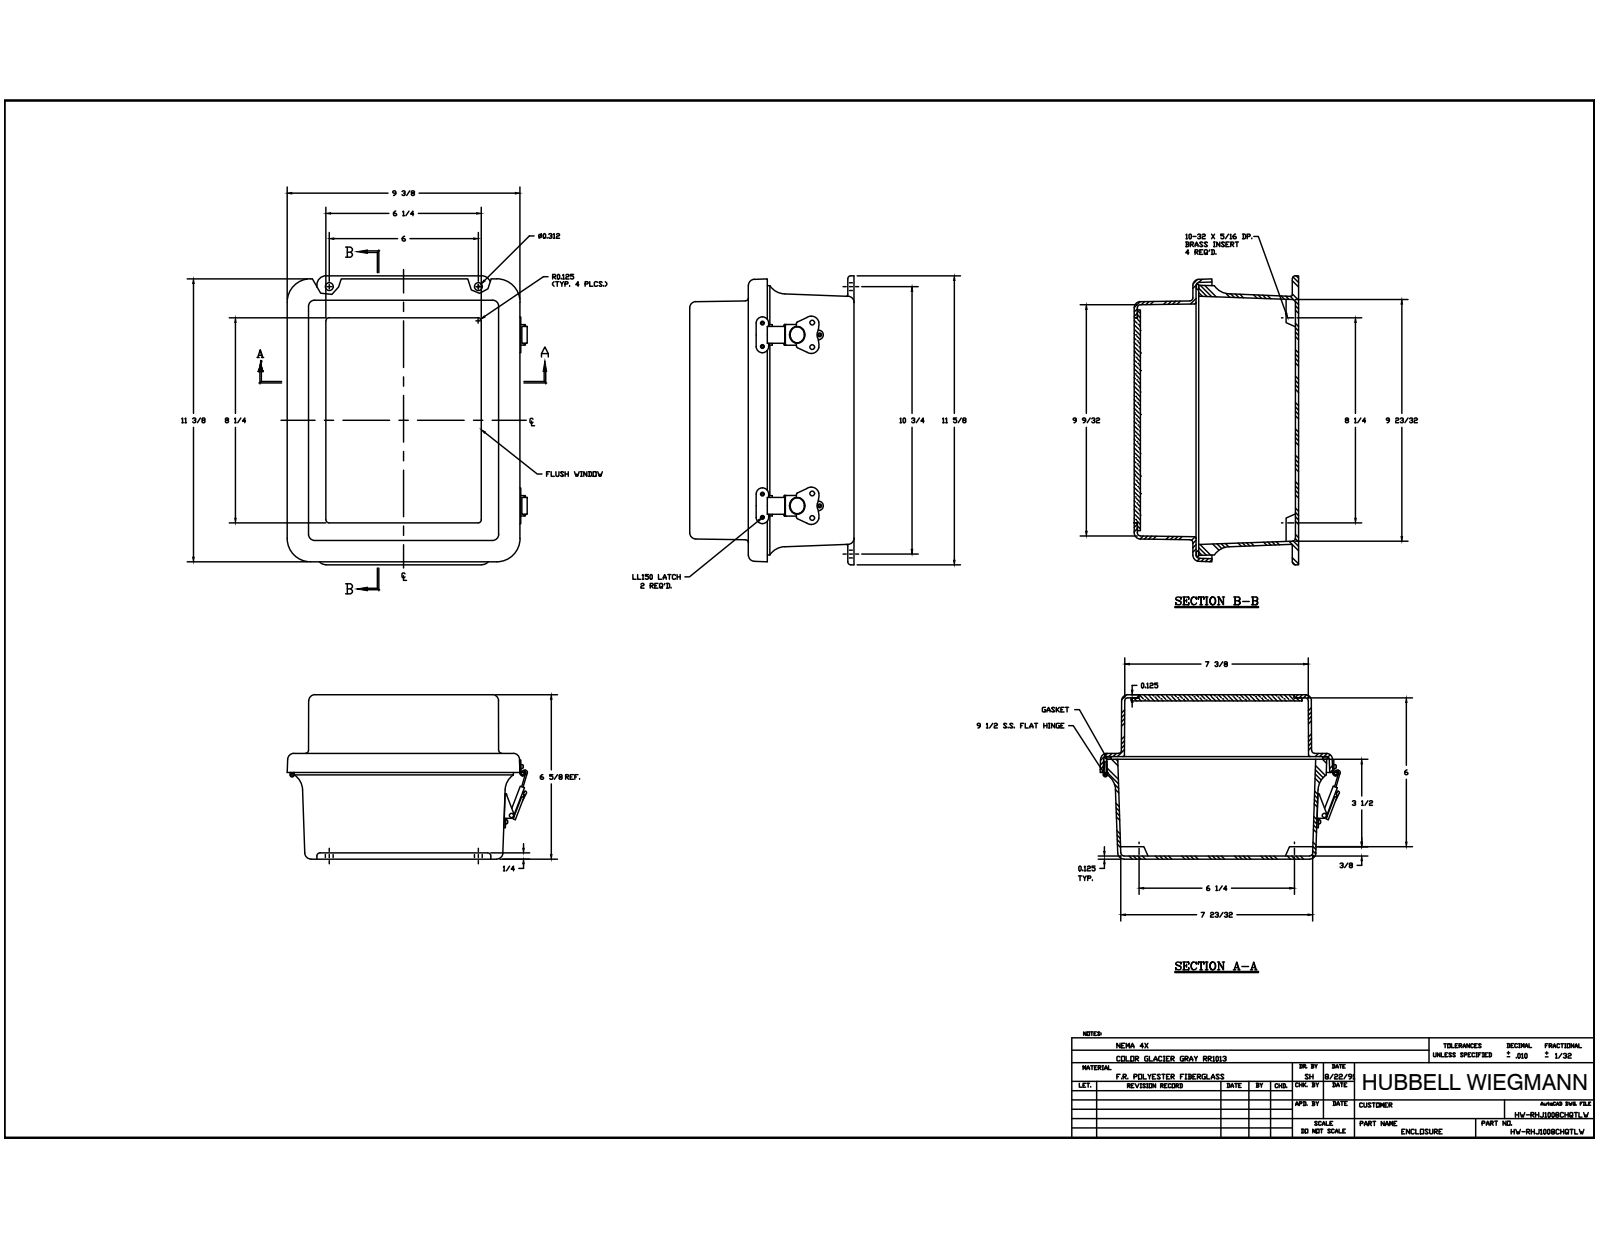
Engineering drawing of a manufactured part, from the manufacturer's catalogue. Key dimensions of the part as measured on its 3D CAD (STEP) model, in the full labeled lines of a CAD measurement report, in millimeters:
Part name (STEP PRODUCT): RJW1008HLL; J1008BHL; J1008HL_11; RMINS45821P_165 (+8 more)
STEP written by: Autodesk Inventor 11 (AUTOMOTIVE_DESIGN)
Units: millimetres
Bodies: 49 solids, 1182 faces (487 planar, 379 cylindrical, 316 other)
Overall size (bounding box): 295.3 × 243.6 × 167.1
Volume: 1 256 000 mm³ · Surface area: 654 200 mm²
Round holes (diameter × count): ⌀3.6 ×12, ⌀4.2 ×4, ⌀5 ×4, ⌀3 ×2, ⌀3.5 ×2, ⌀4.6 ×2, ⌀4.6 ×2, ⌀4.9 ×2, ⌀13.5 ×2, ⌀2.7 ×1
Round bosses / shafts (diameter × count): ⌀6.4 ×16, ⌀3.2 ×16, ⌀6.9 ×4, ⌀14.8 ×2, ⌀13.3 ×2, ⌀5.3 ×2, ⌀4.7 ×2, ⌀3.3 ×2
Partial cylindrical surfaces — rounded edges, fillets, slot ends (radius × count): R3.2 ×28, R0.8 ×20, R2 ×19, R6.4 ×14, R0.9 ×8, R1 ×8, R1.1 ×8, R1.2 ×8
Main face-to-face distances: 3.2, 160.8, 6.4, 167.1, 163.9, 157.6, 104, 56.8, 3.2, 100.8
Hole centre spacings: 177.8, 3, 15.6, 15.7, 36.9, 55.3, 177.8, 178
